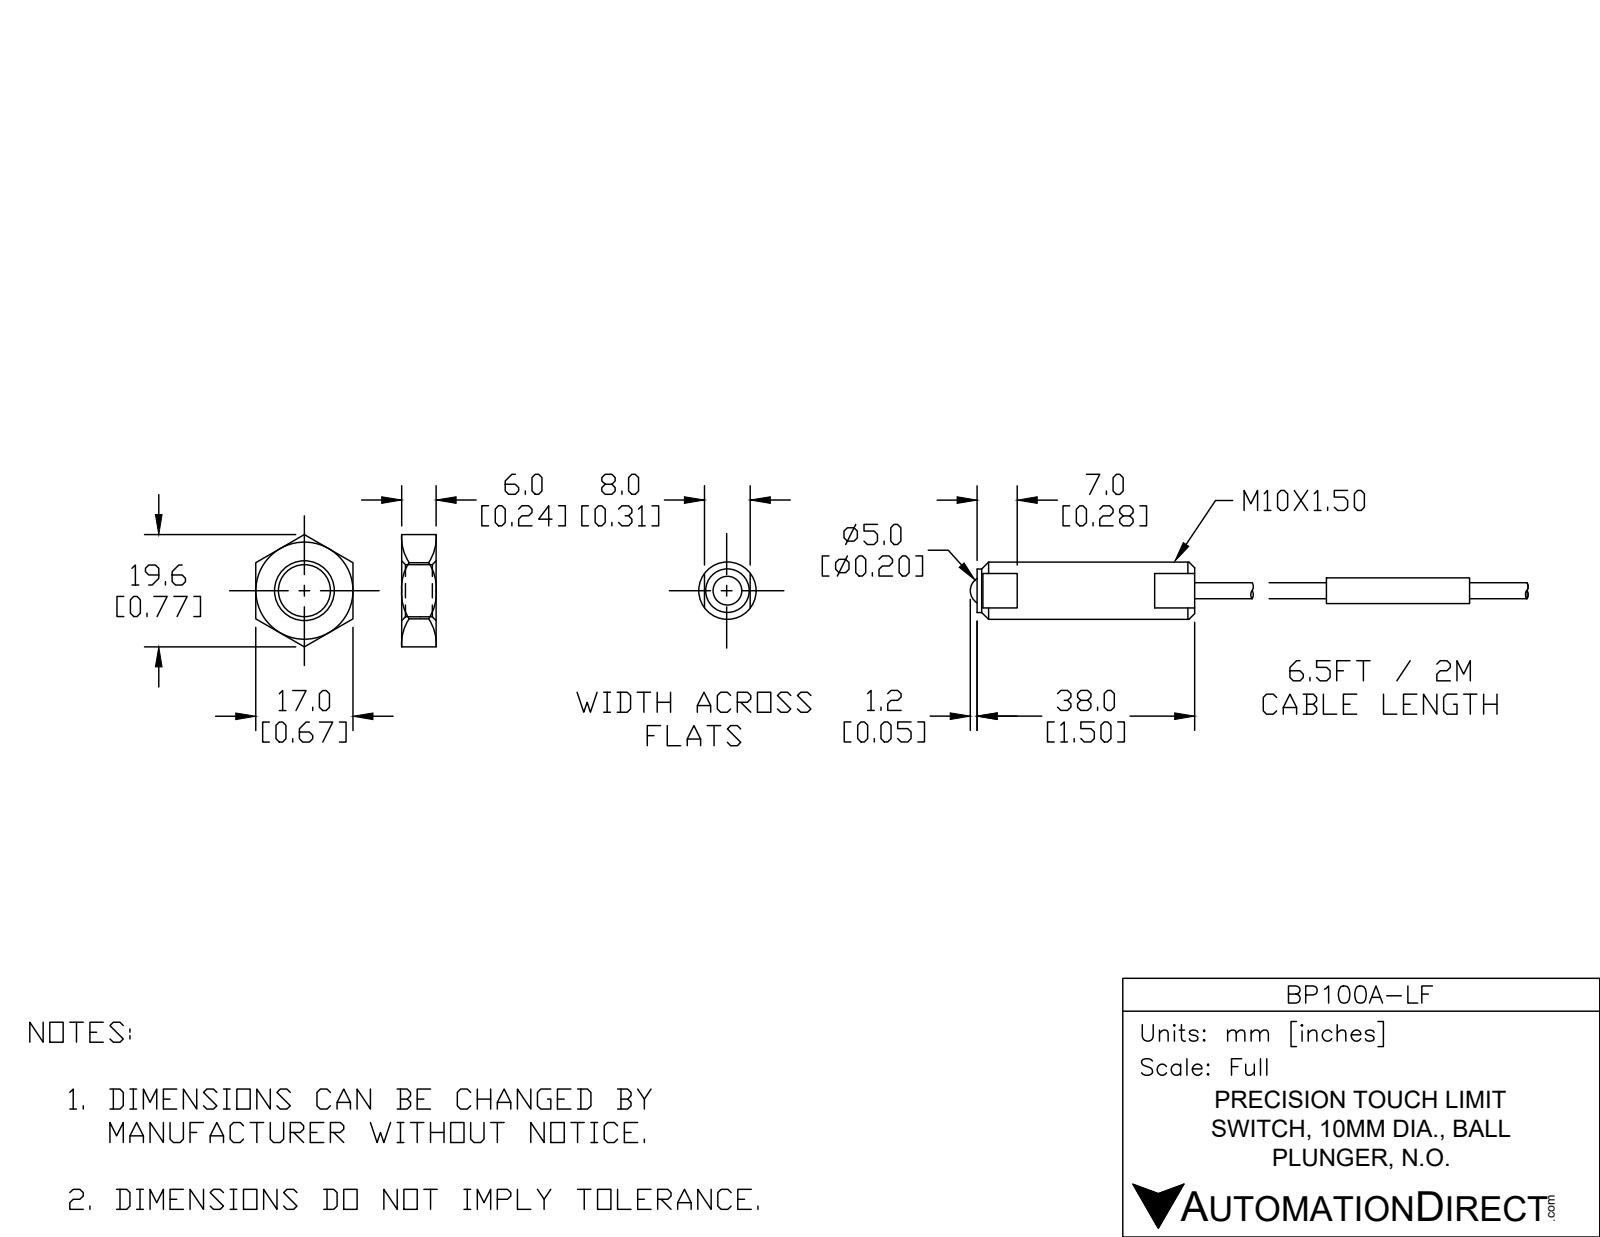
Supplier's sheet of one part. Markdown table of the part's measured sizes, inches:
| quantity | value |
| --- | --- |
| part name | BP100A-LF |
| STEP written by | SolidWorks 2017 (CONFIG_CONTROL_DESIGN) |
| units | inches |
| bodies | 2 solids, 130 faces (15 planar, 58 cylindrical, 57 other) |
| overall size | 3.827 × 0.394 × 0.394 |
| volume | 0.183 in³ |
| surface area | 3.718 in² |
| round bosses / shafts (diameter × count) | 0.394 × 1, 0.299 × 1, 0.177 × 1, 0.11 × 1 |
| main face-to-face distances | 0.315, 1.496, 0.413, 0.492, 2.402, 3.386, 0.906, 1.89, 0.984, 0.276 |
